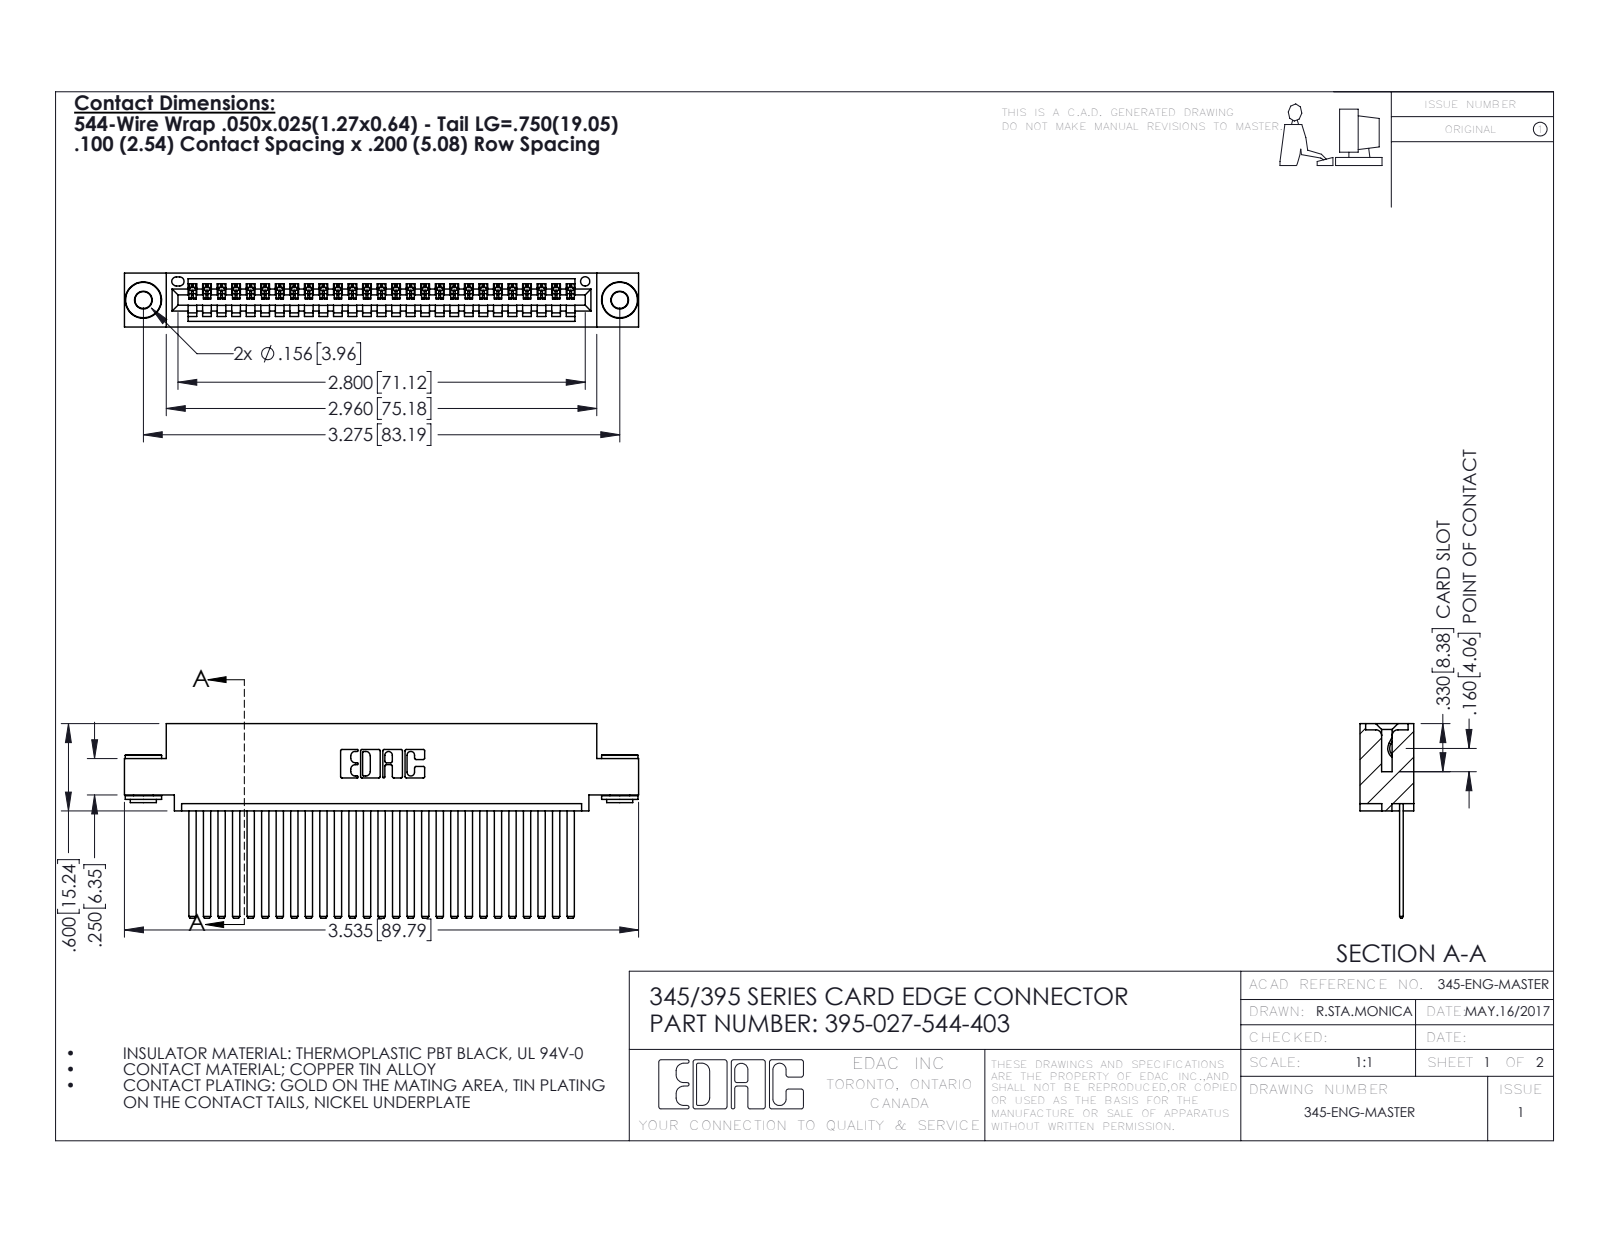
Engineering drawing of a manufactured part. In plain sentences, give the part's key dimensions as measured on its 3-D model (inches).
The part is named "345-292-001_345-293-144; 395-027-544-403; 345-250-002_345-250-002-102; 345 Part_0.110 Offset - 0.156 Dia-TH". Its 3-D file was written by "SolidWorks 2016 (CONFIG_CONTROL_DESIGN)". It is 30 solids with 1572 faces: 1066 planar, 498 cylindrical and 8 other. Overall it measures 3.535 by 1.337 by 0.37 inches. Its volume is 0.529 cubic inches and its surface area 19.44 square inches. Round holes: 2 of diameter 0.116, 2 of diameter 0.156, 1 of diameter 0.064. Round bosses or shafts: 2 of diameter 0.25, 2 of diameter 0.18, 2 of diameter 0.136. Partial cylindrical surfaces (rounded edges, fillets, slot ends): 54 of radius 0.006, 22 of radius 0.01, 6 of radius 0.007, 6 of radius 0.031, 3 of radius 0.026, 2 of radius 0.031, 2 of radius 0.04, 1 of radius 0.014. The main face-to-face distances are 0.072, 0.298, 0.025, 0.098, 0.272, 0.37, 0.2, 0.225, 0.149, 0.072. The hole center spacings are 0.27, 3.04, 3.275.
